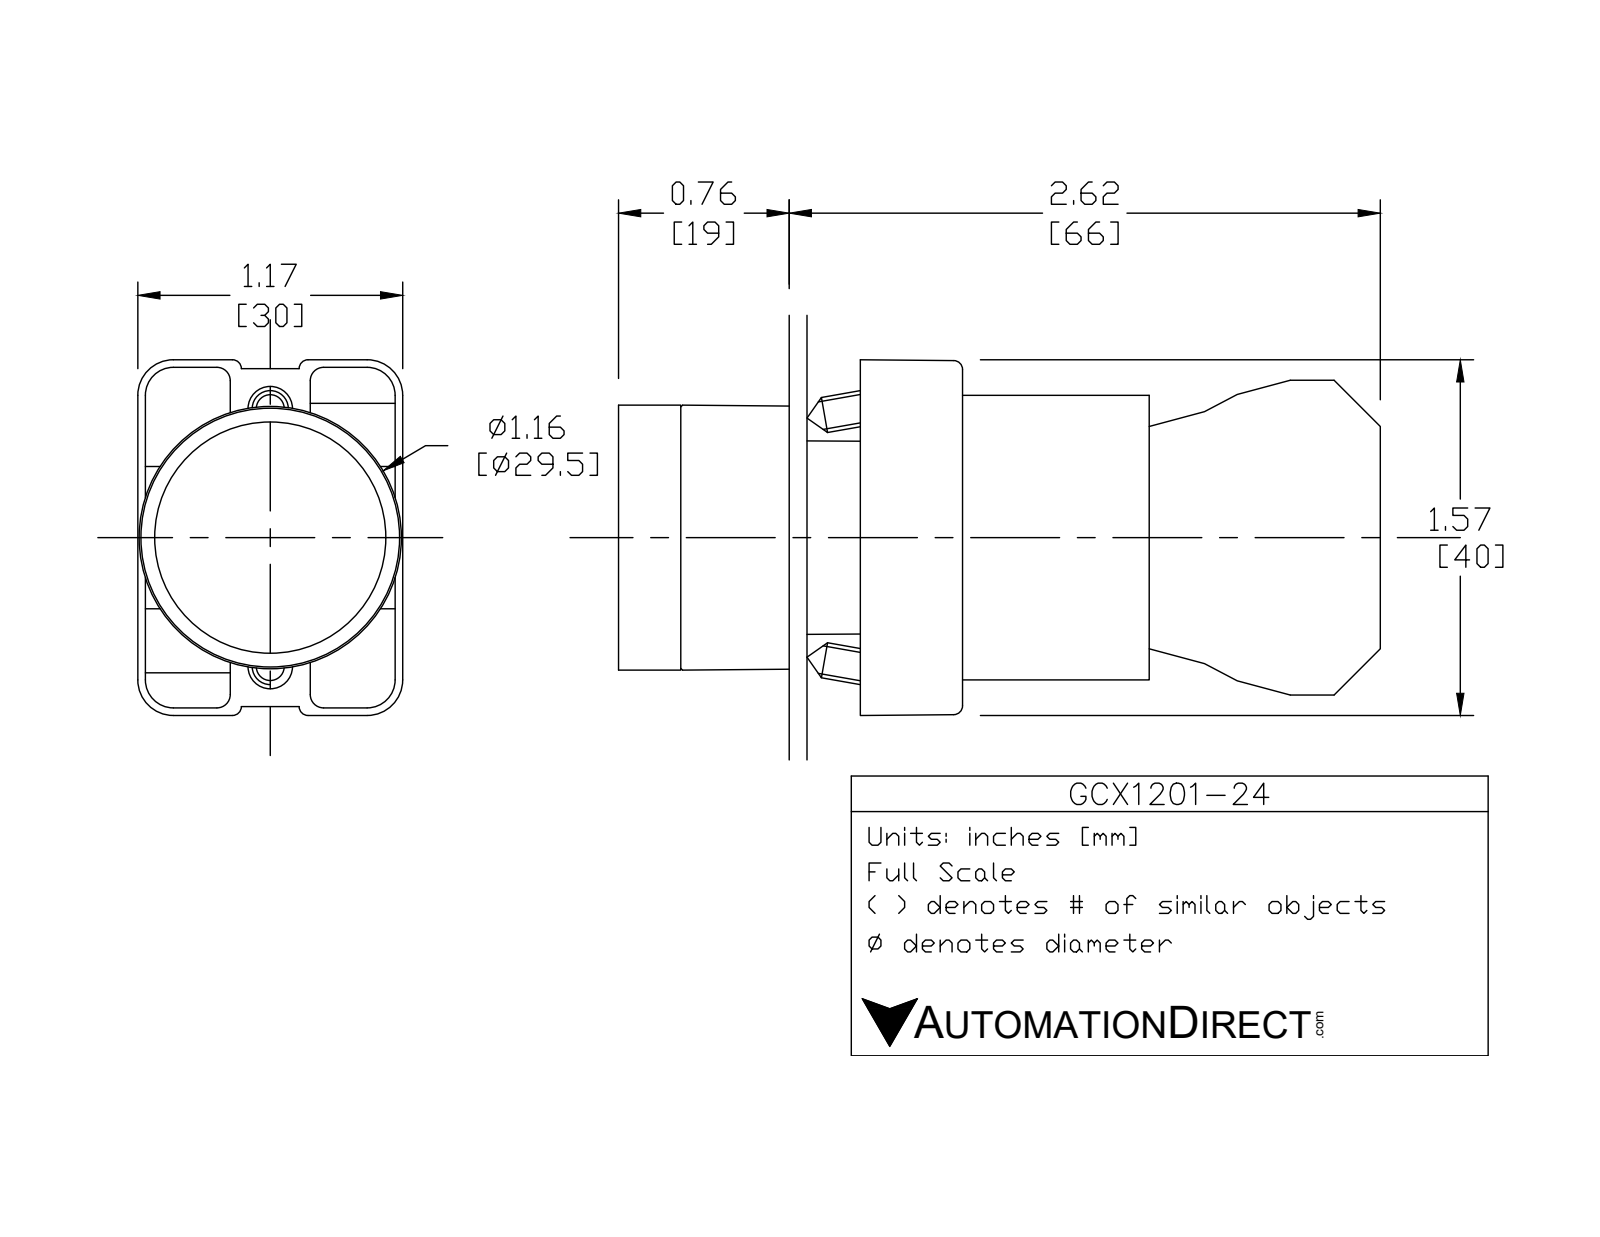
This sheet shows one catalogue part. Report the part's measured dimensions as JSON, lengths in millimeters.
{"part_name": "ecx1029; GCX1201 OPERATOR; ECX1050; GCX1201-24 (+1 more)", "step_written_by": "SolidWorks 2016 (AUTOMOTIVE_DESIGN)", "units": "millimeters", "bodies": {"solids": 8, "faces": 431, "planar": 252, "cylindrical": 148, "other": 31}, "overall_size": [84.3, 40.2, 29.9], "volume_mm3": 45790, "surface_area_mm2": 25000, "round_holes": [[2, 2], [3.1, 2], [3.3, 2], [2.2, 1], [5, 1], [11.9, 1], [22.3, 1], [22.6, 1], [26, 1]], "round_bosses_or_shafts": [[4, 4], [29.8, 1], [25.5, 1], [24, 1], [21.7, 1], [19.8, 1], [12.8, 1]], "partial_cylinders_radius": [[1.5, 24], [1, 12], [3.1, 12], [4, 12], [1, 8], [3.3, 2], [0.5, 1], [1.6, 1]], "face_to_face_distances": [21, 51.3, 30.3, 14.7, 29.7, 0.8, 7, 0.8, 19, 14.6], "hole_center_spacings": [6, 13.8, 12, 12.4]}
